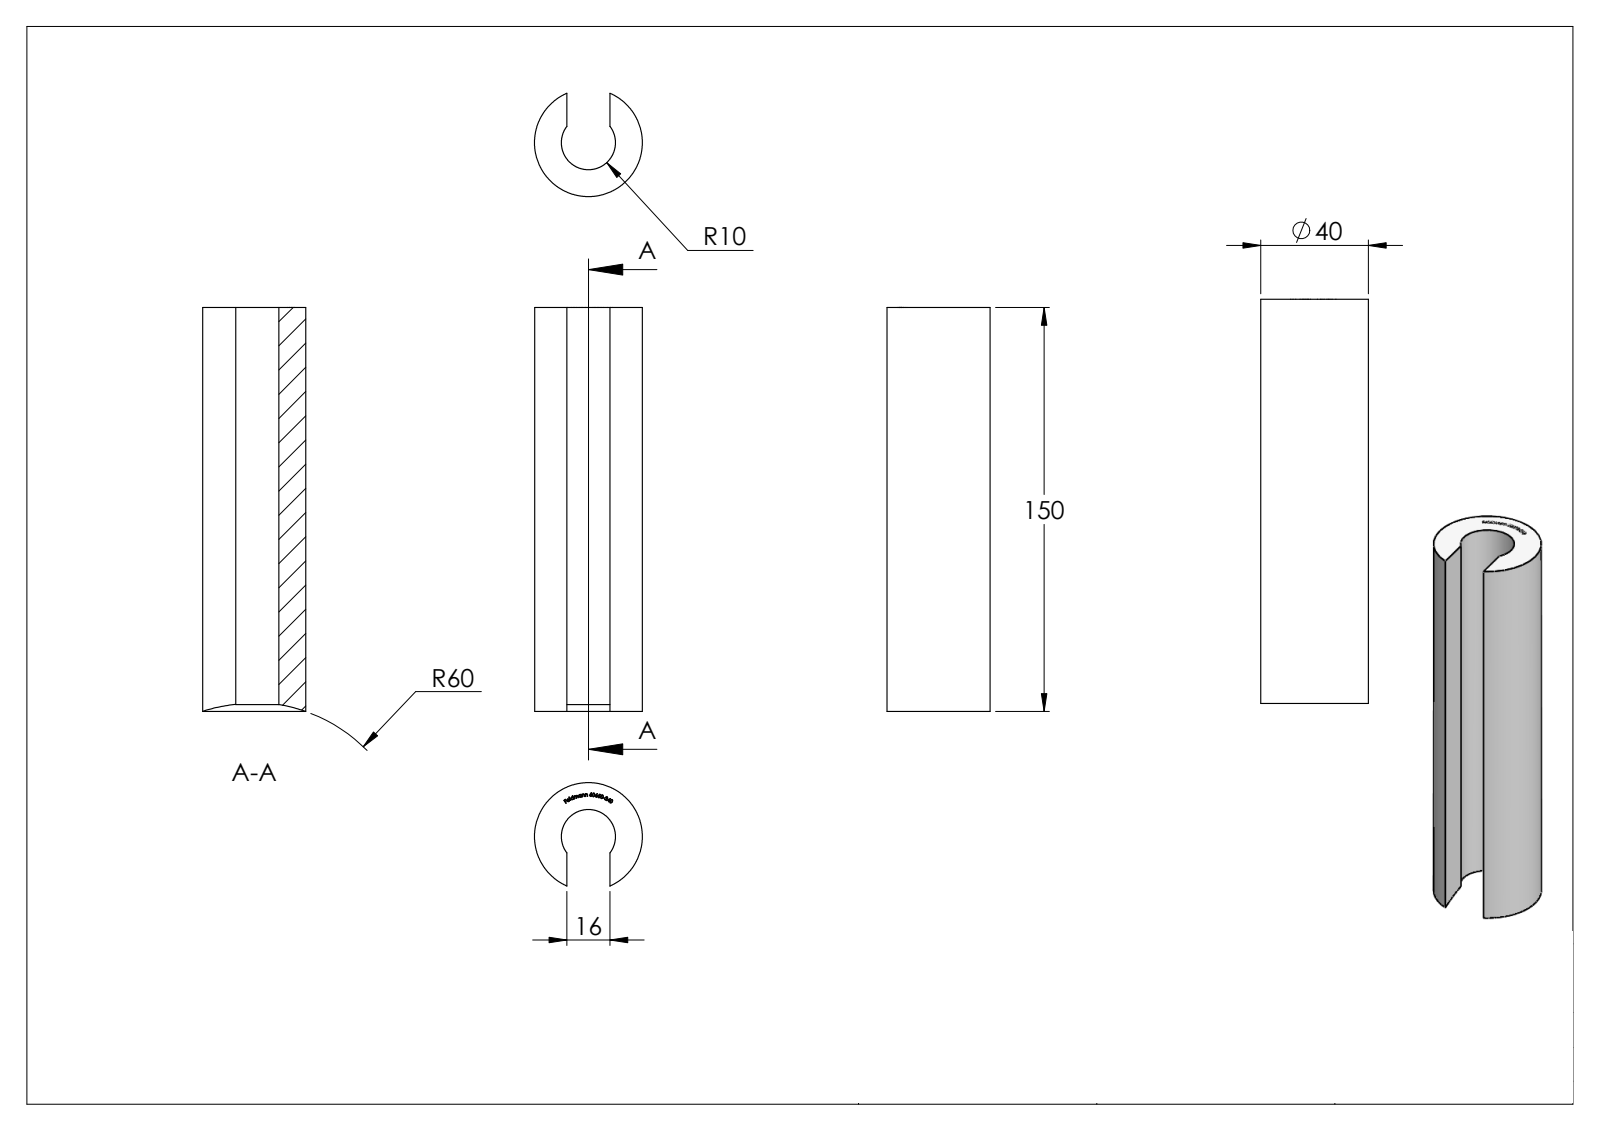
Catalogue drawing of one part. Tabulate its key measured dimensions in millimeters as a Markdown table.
| quantity | value |
| --- | --- |
| part name | 60650-240 |
| STEP written by | SolidWorks 2015 (CONFIG_CONTROL_DESIGN) |
| units | millimeters |
| bodies | 1 solid, 231 faces (118 planar, 4 cylindrical, 109 other) |
| overall size | 150 × 40 × 38.33 |
| volume | 114 813 mm³ |
| surface area | 28 153 mm² |
| round bosses / shafts (diameter × count) | 40 × 1 |
| partial cylindrical surfaces (radius × count) | 10 × 1 |
| main face-to-face distances | 16, 0.54, 0.66, 0.72, 0.67, 0.73, 1.45, 1.32, 0.41, 0.85 |
